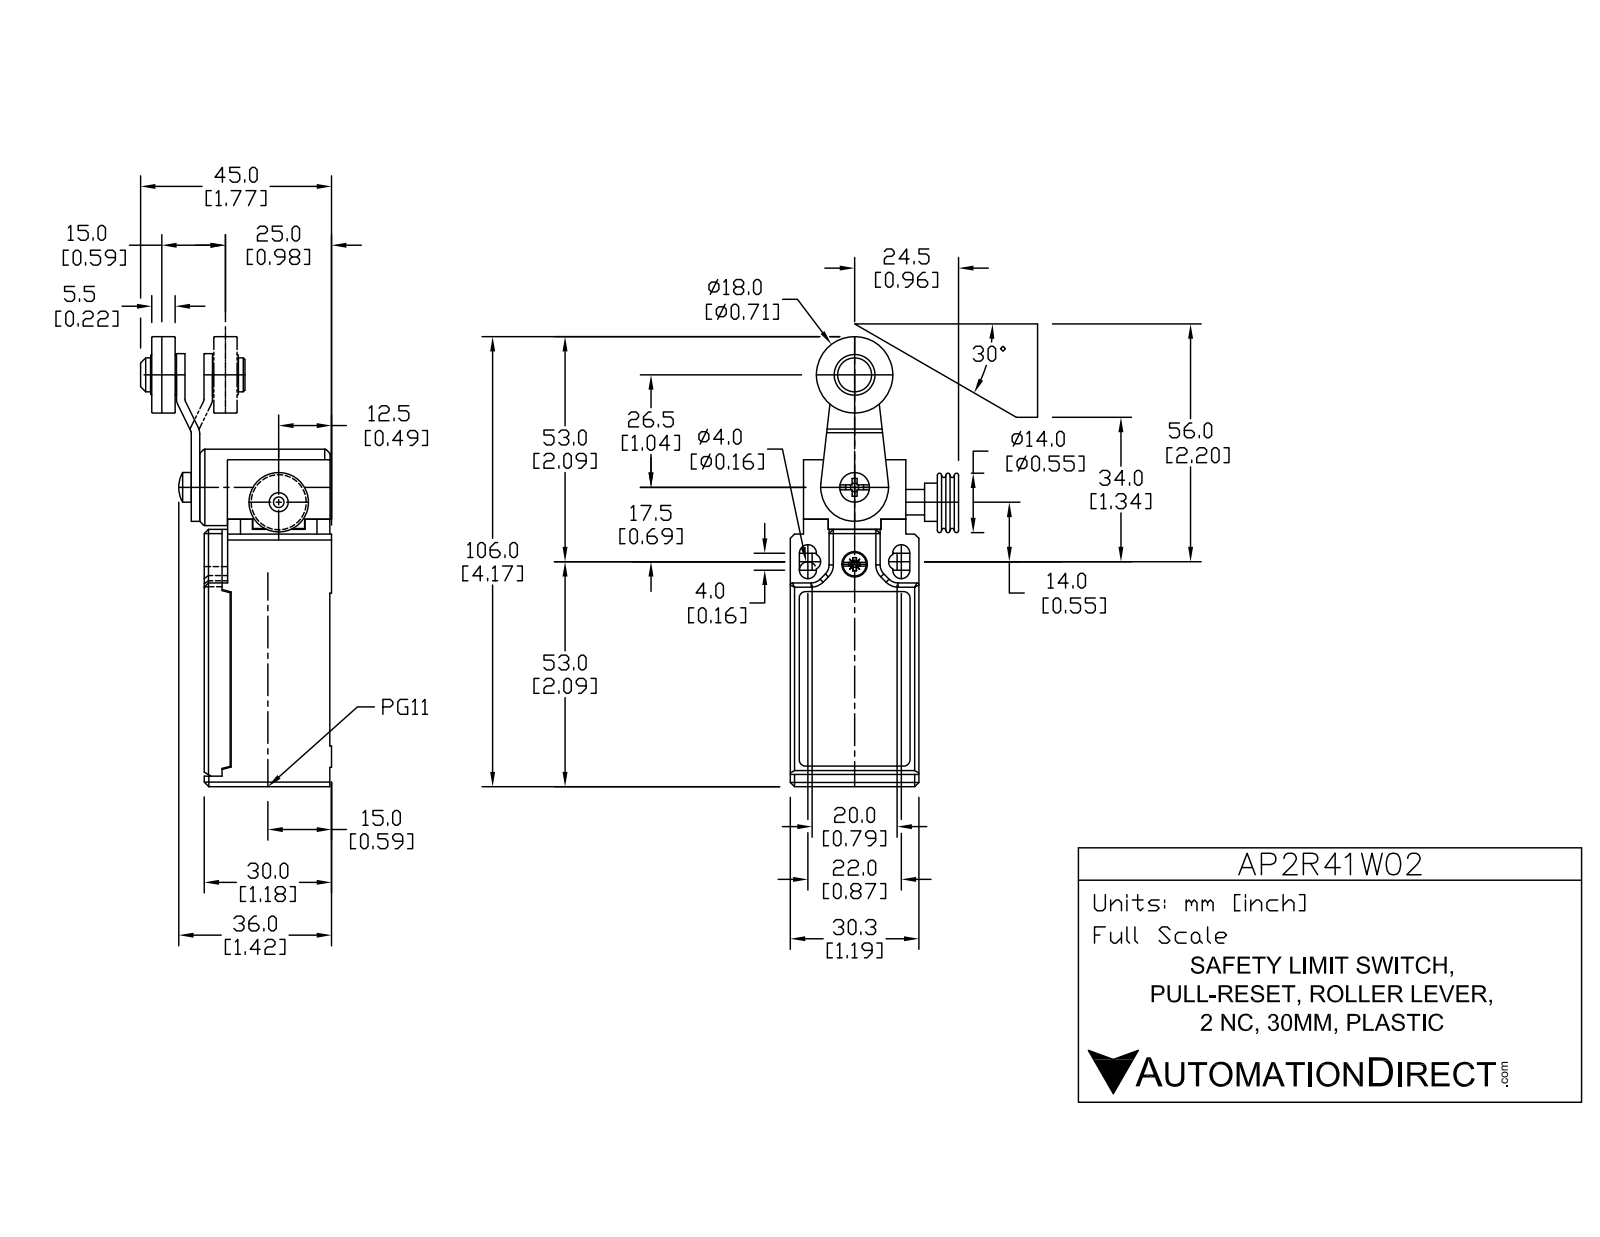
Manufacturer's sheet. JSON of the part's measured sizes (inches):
{"part_name": "AP2R41W02", "step_written_by": "SolidWorks 2017 (AUTOMOTIVE_DESIGN)", "units": "inches", "bodies": {"solids": 3, "faces": 255, "planar": 108, "cylindrical": 84, "other": 63}, "overall_size": [4.232, 1.717, 1.543], "volume_in3": 4.09, "surface_area_in2": 26.01, "round_holes": [[0.669, 1], [0.748, 1]], "round_bosses_or_shafts": [[0.22, 4], [0.217, 3], [0.709, 2], [0.587, 1], [0.531, 1], [0.386, 1], [0.374, 1], [0.315, 1]], "partial_cylinders_radius": [[0.02, 8], [0.079, 6], [0.118, 6], [0.039, 4], [0.197, 1], [0.315, 1], [0.394, 1], [0.4, 1]], "face_to_face_distances": [1.193, 1.165, 0.124, 1.069, 0.945, 0.236, 1.181, 0.016, 0.276, 2.444]}
